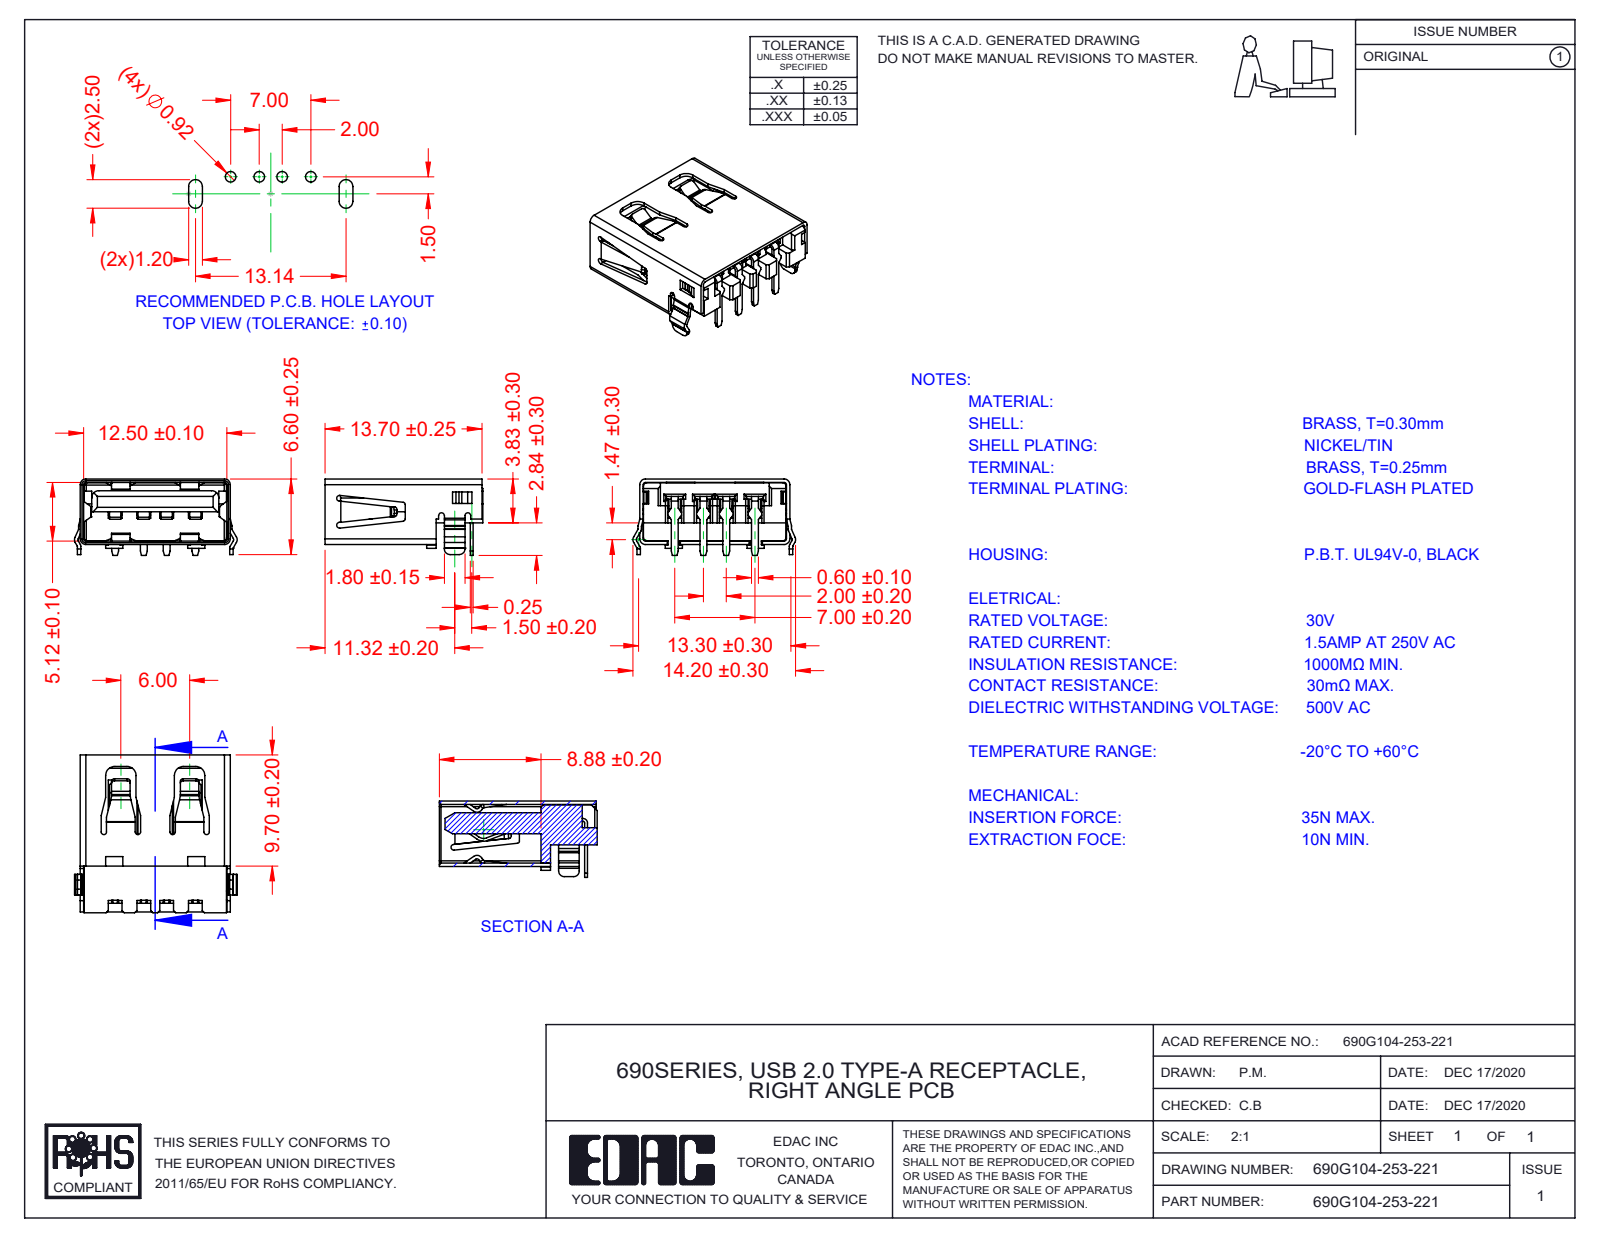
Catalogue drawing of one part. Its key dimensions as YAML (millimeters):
part_name: "Contact 690G104-253-22X; Shell 690G104-253-22X; Insulator 690G104-253-22X_Black; 690G104-253-221"
step_written_by: "SolidWorks 2020 (AUTOMOTIVE_DESIGN)"
units: millimeters
bodies: {solids: 6, faces: 738, planar: 554, cylindrical: 164, other: 20}
overall_size: [14.2, 13.78, 6.67]
volume: 407
surface_area: 1712
partial_cylinders:
  - {radius: 0.25, count: 22}
  - {radius: 0.2, count: 14}
  - {radius: 0.5, count: 14}
  - {radius: 0.1, count: 10}
  - {radius: 0.6, count: 6}
  - {radius: 0.3, count: 5}
  - {radius: 0.9, count: 5}
  - {radius: 0.8, count: 4}
face_to_face_distances: [5.42, 2.56, 2.86, 5.72, 5.12, 12.8, 1.22, 0.5, 1.52, 4.2]
